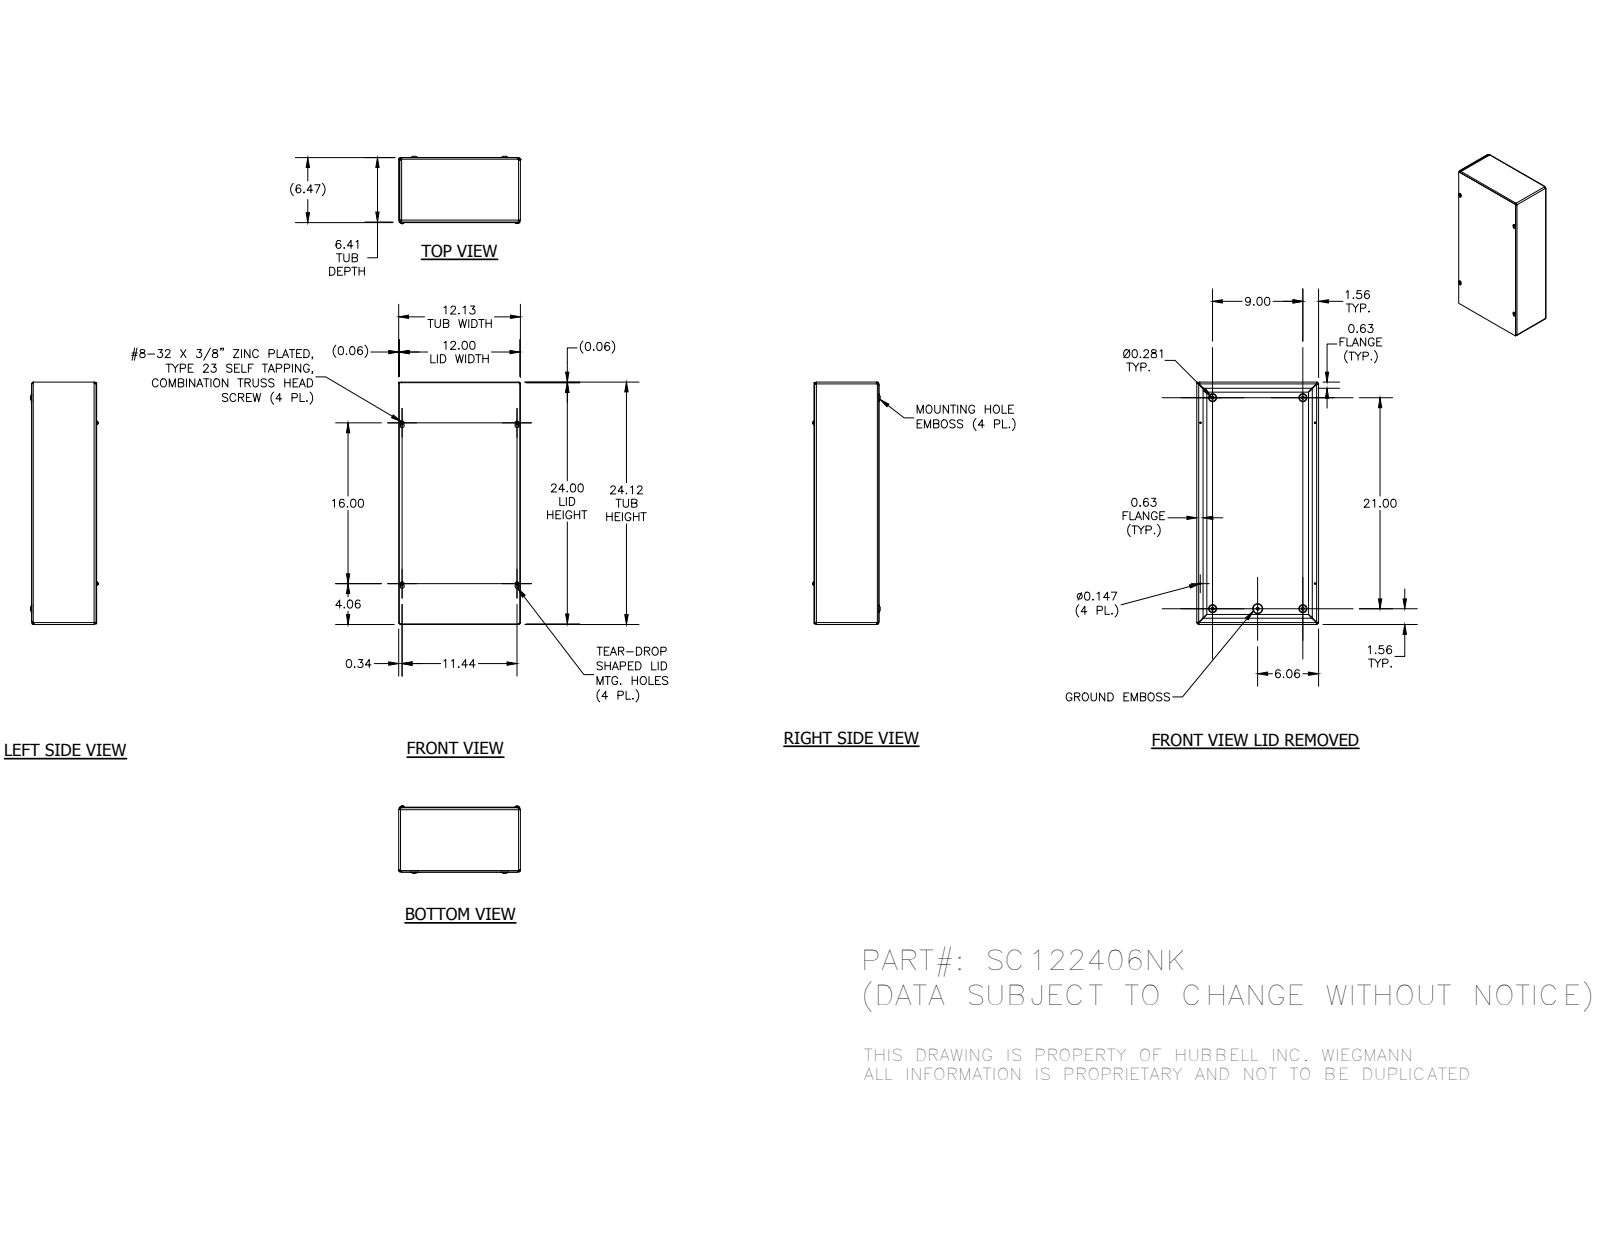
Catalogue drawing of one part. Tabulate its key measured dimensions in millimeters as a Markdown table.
| quantity | value |
| --- | --- |
| part name | SC1224BKP; SC122406NKWRA; SC1224LID; 34056 (+1 more) |
| STEP written by | Autodesk Inventor 2014 (AUTOMOTIVE_DESIGN) |
| units | millimeters |
| bodies | 7 solids, 357 faces (132 planar, 67 cylindrical, 158 other) |
| overall size | 612.77 × 307.98 × 170 |
| volume | 1 143 000 mm³ |
| surface area | 1 462 000 mm² |
| round holes (diameter × count) | 3.73 × 4, 7.62 × 4, 4.19 × 1 |
| round bosses / shafts (diameter × count) | 9.75 × 4, 4.17 × 4, 5.8 × 1 |
| partial cylindrical surfaces (radius × count) | 3.17 × 12, 4.75 × 8, 1.4 × 4, 1.57 × 4, 2.38 × 4, 2.97 × 4, 3.15 × 4, 3.96 × 4 |
| main face-to-face distances | 1.57, 161.12, 162.69, 1.59, 162.71, 164.28, 1.58, 307.98, 306.41, 306.4 |
| hole center spacings | 470.92, 536.82, 70.64, 70.65, 114.3, 228.6, 267.2, 267.21 |
